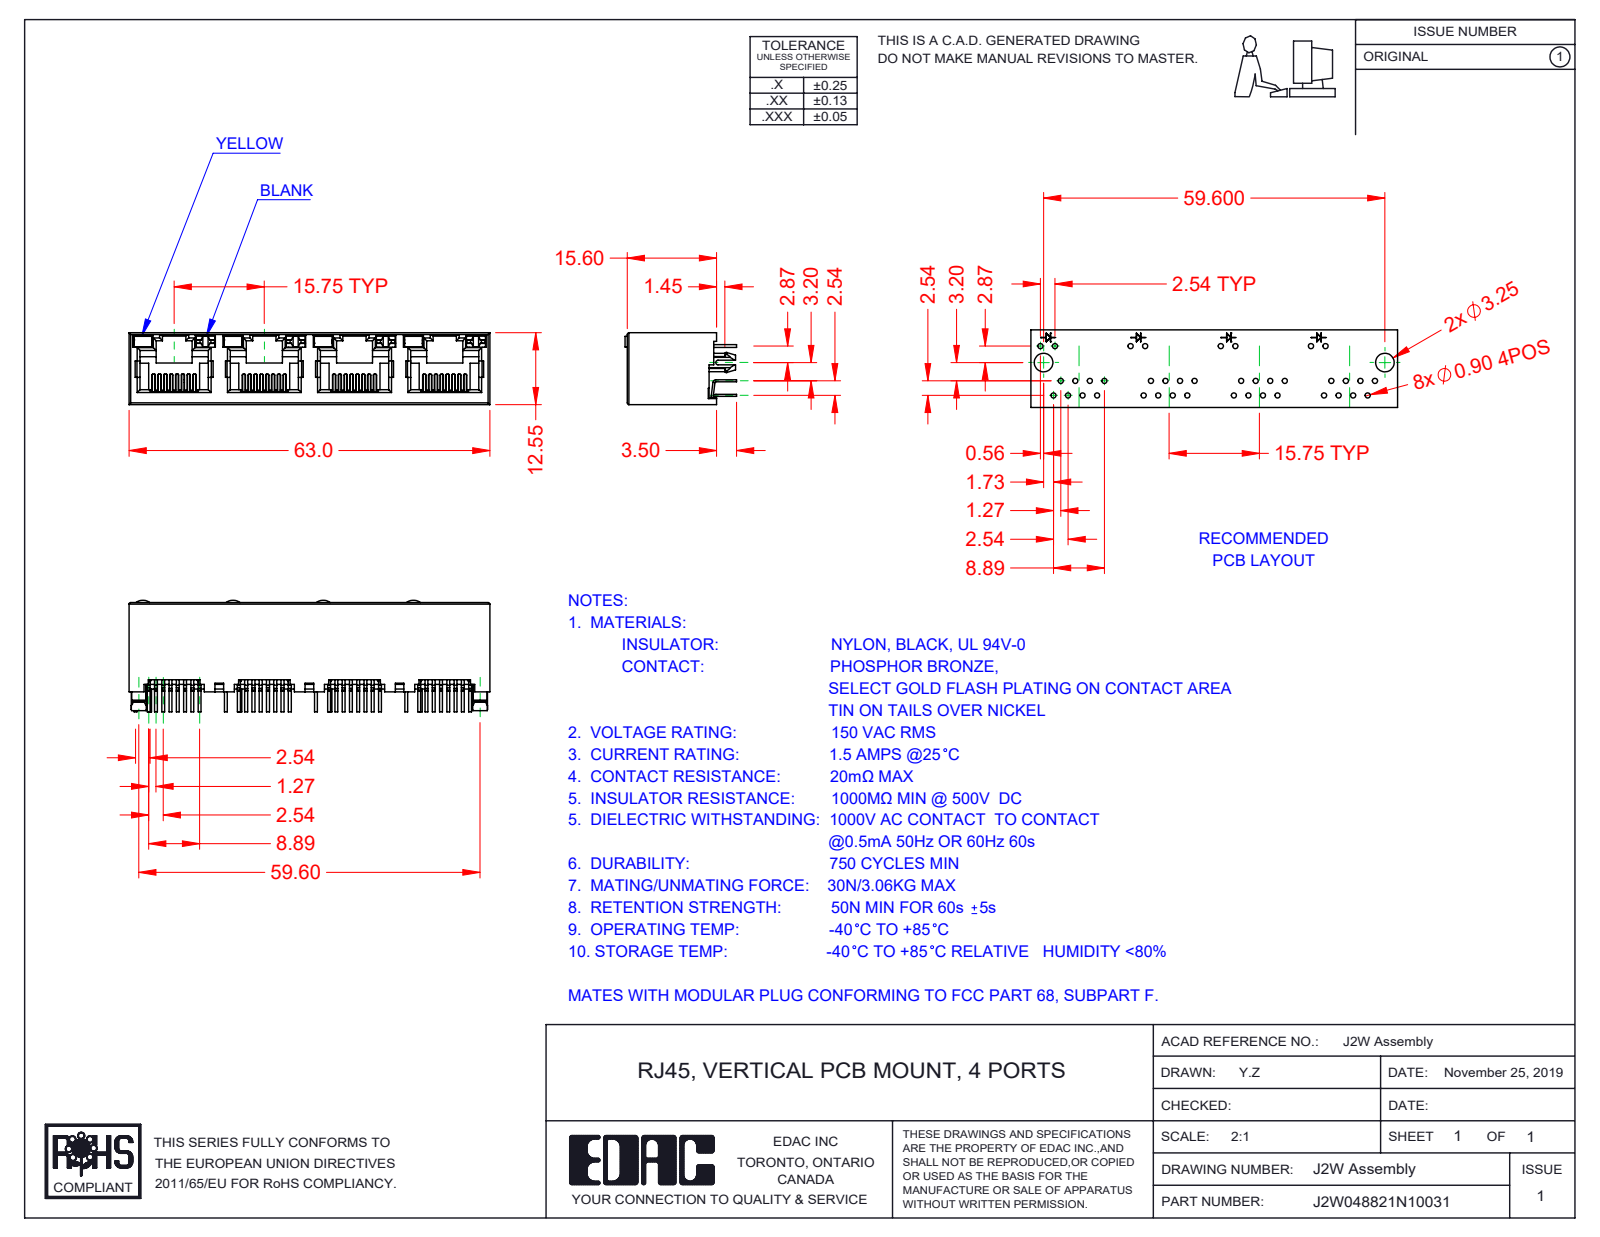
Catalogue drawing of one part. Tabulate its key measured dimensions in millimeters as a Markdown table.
| quantity | value |
| --- | --- |
| part name | 2W Contacts; 2W LED LH_1-Yellow; J2W048821N10031; 2W Contact Lock (+2 more) |
| STEP written by | SolidWorks 2020 (CONFIG_CONTROL_DESIGN) |
| units | millimeters |
| bodies | 41 solids, 3007 faces (2508 planar, 441 cylindrical, 58 other) |
| overall size | 63 × 19.5 × 12.55 |
| volume | 5 212 mm³ |
| surface area | 12 695 mm² |
| partial cylindrical surfaces (radius × count) | 0.15 × 64, 0.2 × 29, 0.5 × 28, 0.3 × 14, 0.45 × 8, 2 × 4, 0.25 × 2, 1.5 × 2 |
| main face-to-face distances | 12.55, 11.9, 0.65, 15.75, 0.36, 1.5, 0.78, 0.6, 11.3, 31.5 |
